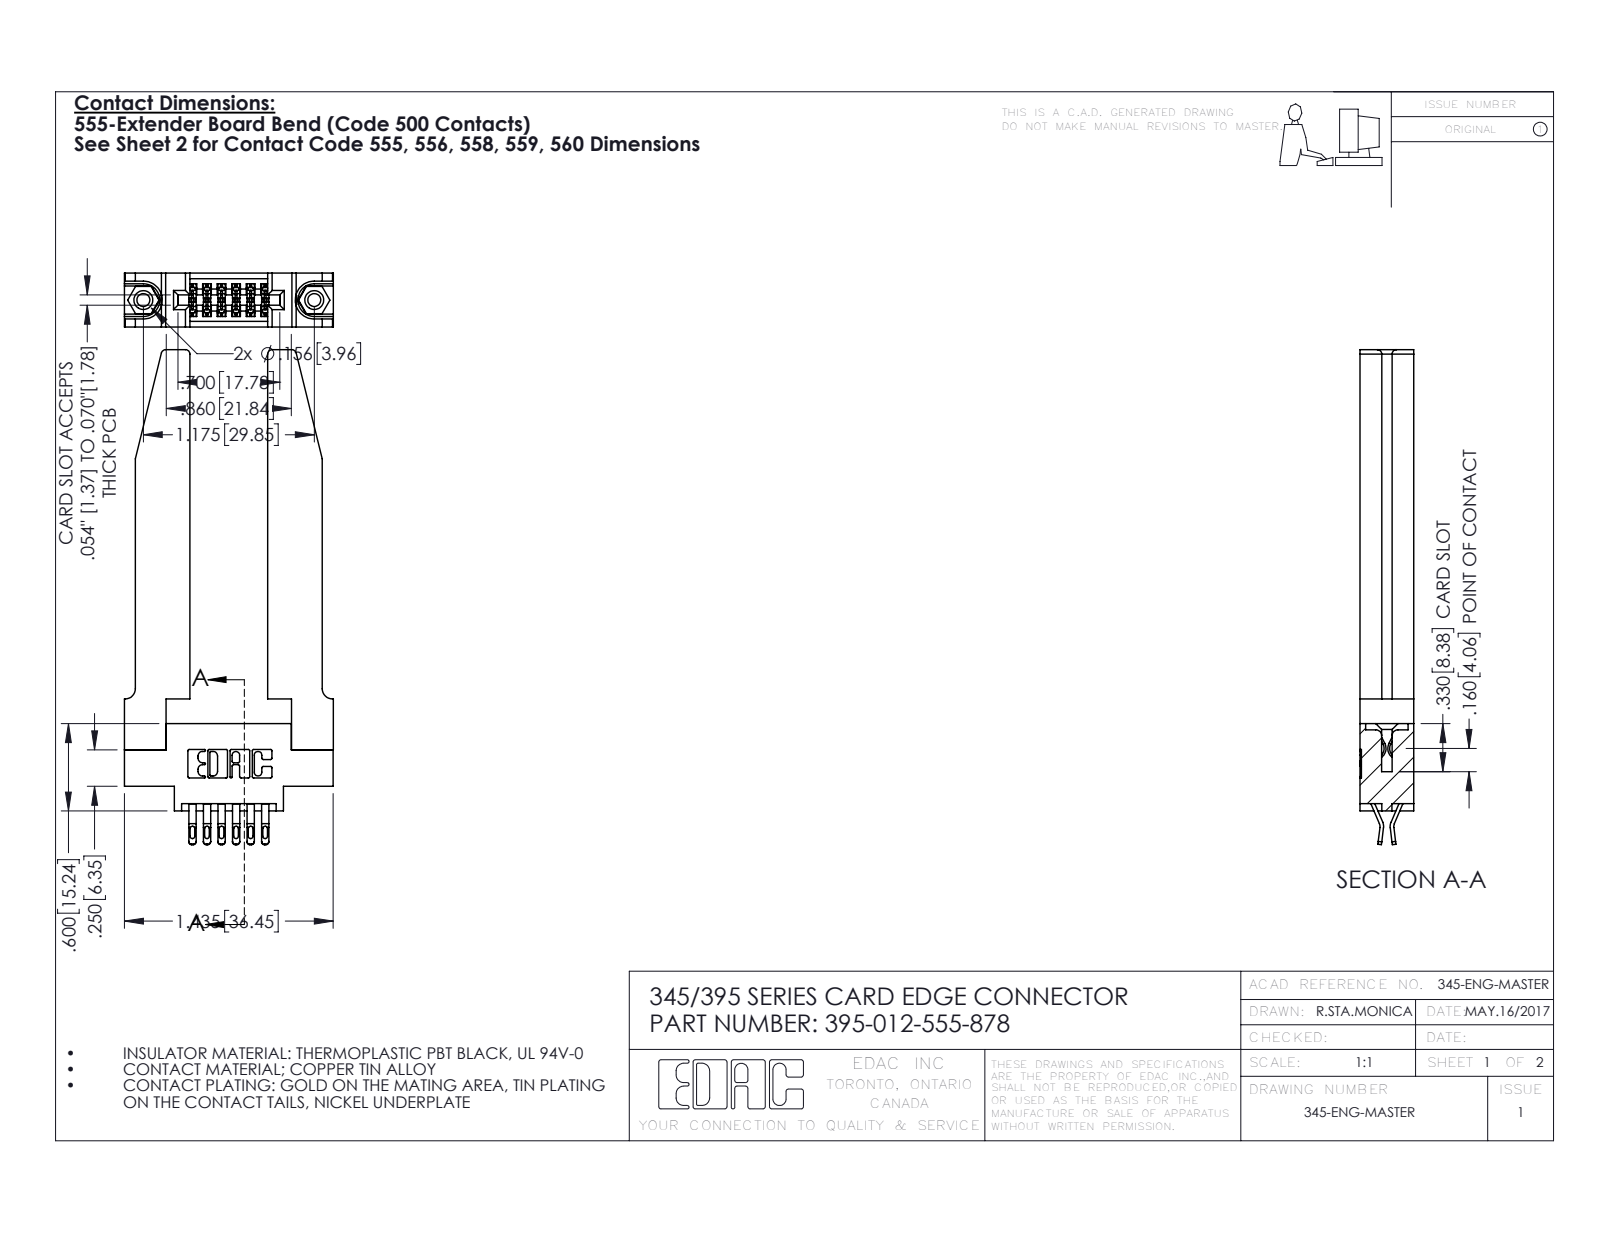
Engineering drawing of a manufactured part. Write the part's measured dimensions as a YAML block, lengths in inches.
part_name: "395-012-555-878; 345-220-078_345-220-078; 345-292-001_555 Tail; 345-250-001_345-250-001-102 (+1 more)"
step_written_by: "SolidWorks 2016 (CONFIG_CONTROL_DESIGN)"
units: inches
bodies: {solids: 17, faces: 1036, planar: 598, cylindrical: 386, other: 52}
overall_size: [3.402, 1.436, 0.37]
volume: 0.665
surface_area: 17.1
round_holes:
  - {diameter: 0.089, count: 2}
  - {diameter: 0.125, count: 2}
  - {diameter: 0.156, count: 2}
  - {diameter: 0.064, count: 1}
round_bosses_or_shafts:
  - {diameter: 0.155, count: 2}
partial_cylinders:
  - {radius: 0.016, count: 30}
  - {radius: 0.02, count: 24}
  - {radius: 0.01, count: 22}
  - {radius: 0.006, count: 18}
  - {radius: 0.03, count: 8}
  - {radius: 0.007, count: 6}
  - {radius: 0.031, count: 6}
  - {radius: 0.026, count: 3}
face_to_face_distances: [0.37, 0.15, 0.22, 0.535, 0.072, 0.148, 0.298, 0.077, 0.095, 0.071]
hole_center_spacings: [0.27, 0.946, 1.175]
